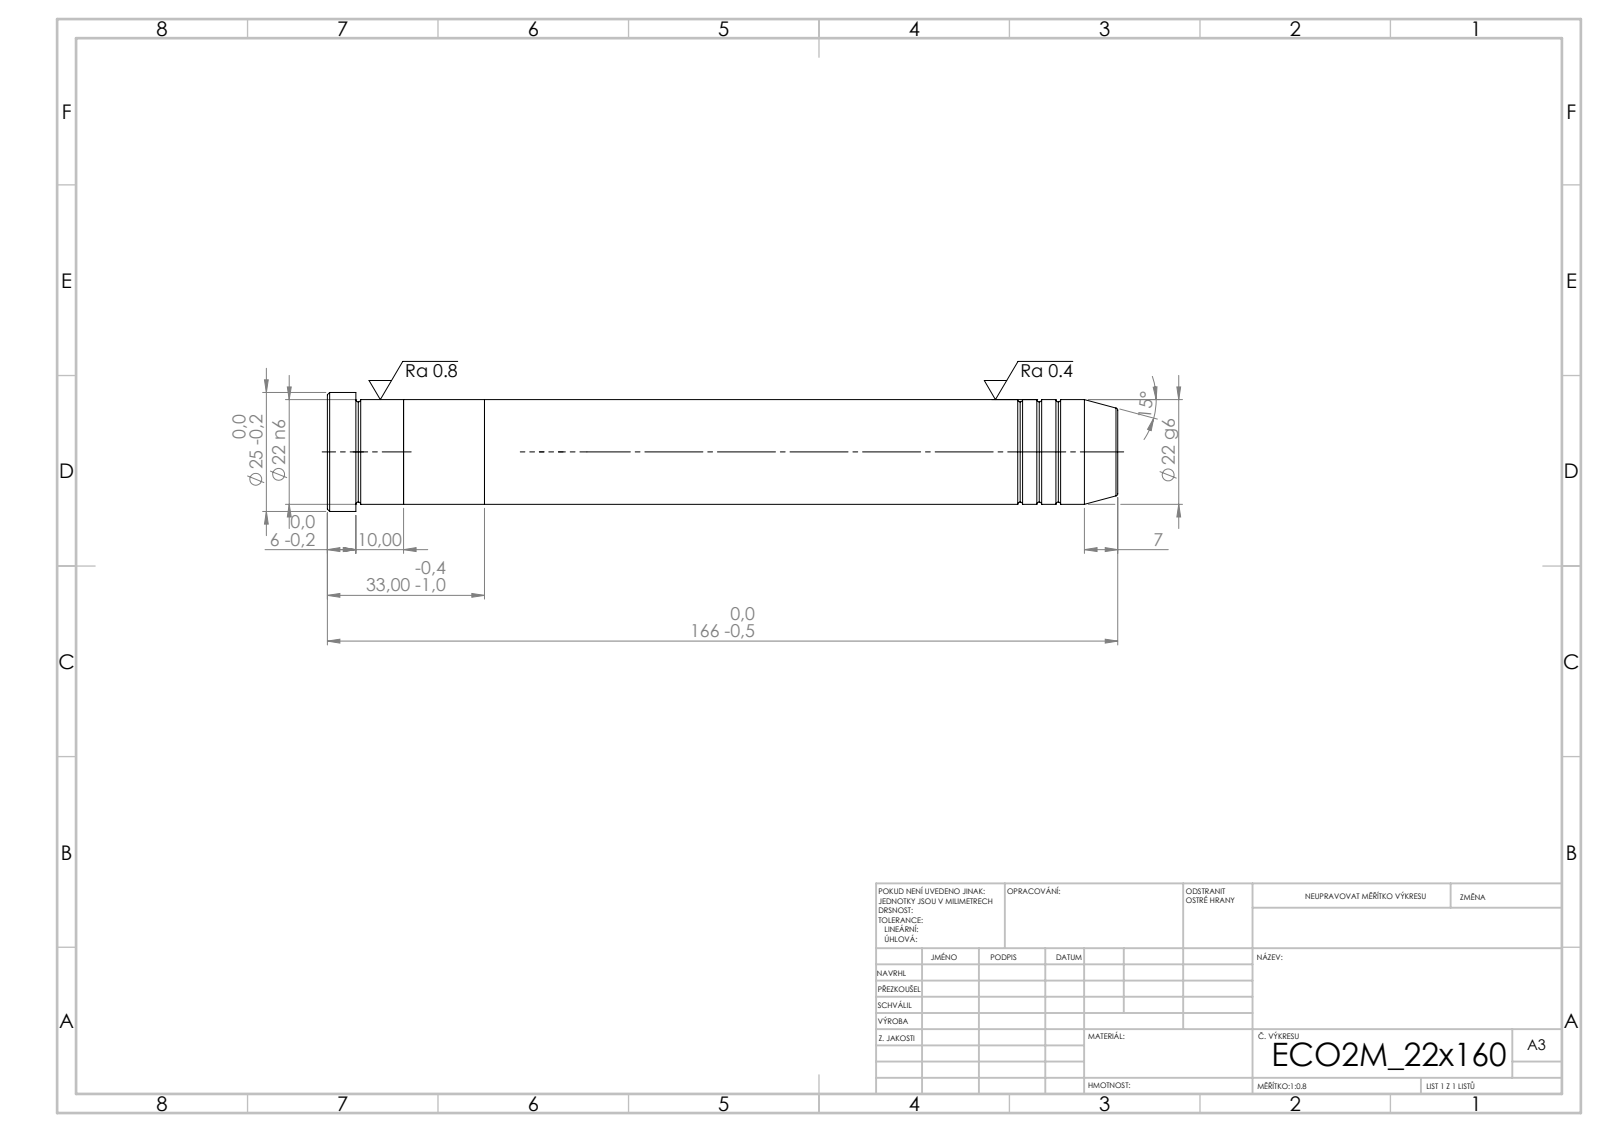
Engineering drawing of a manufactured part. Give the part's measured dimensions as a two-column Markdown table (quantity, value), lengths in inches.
| quantity | value |
| --- | --- |
| STEP written by | SolidWorks 2019 (CONFIG_CONTROL_DESIGN) |
| units | inches |
| bodies | 3 solids, 43 faces (7 planar, 14 cylindrical, 22 other) |
| overall size | 6.535 × 0.984 × 0.984 |
| volume | 3.858 in³ |
| surface area | 21.7 in² |
| round bosses / shafts (diameter × count) | 0.984 × 1, 0.866 × 1 |
| main face-to-face distances | 0.669, 1.299, 0.63, 5.236, 5.906, 6.535, 6.299, 1.063, 0.394, 0.236 |
